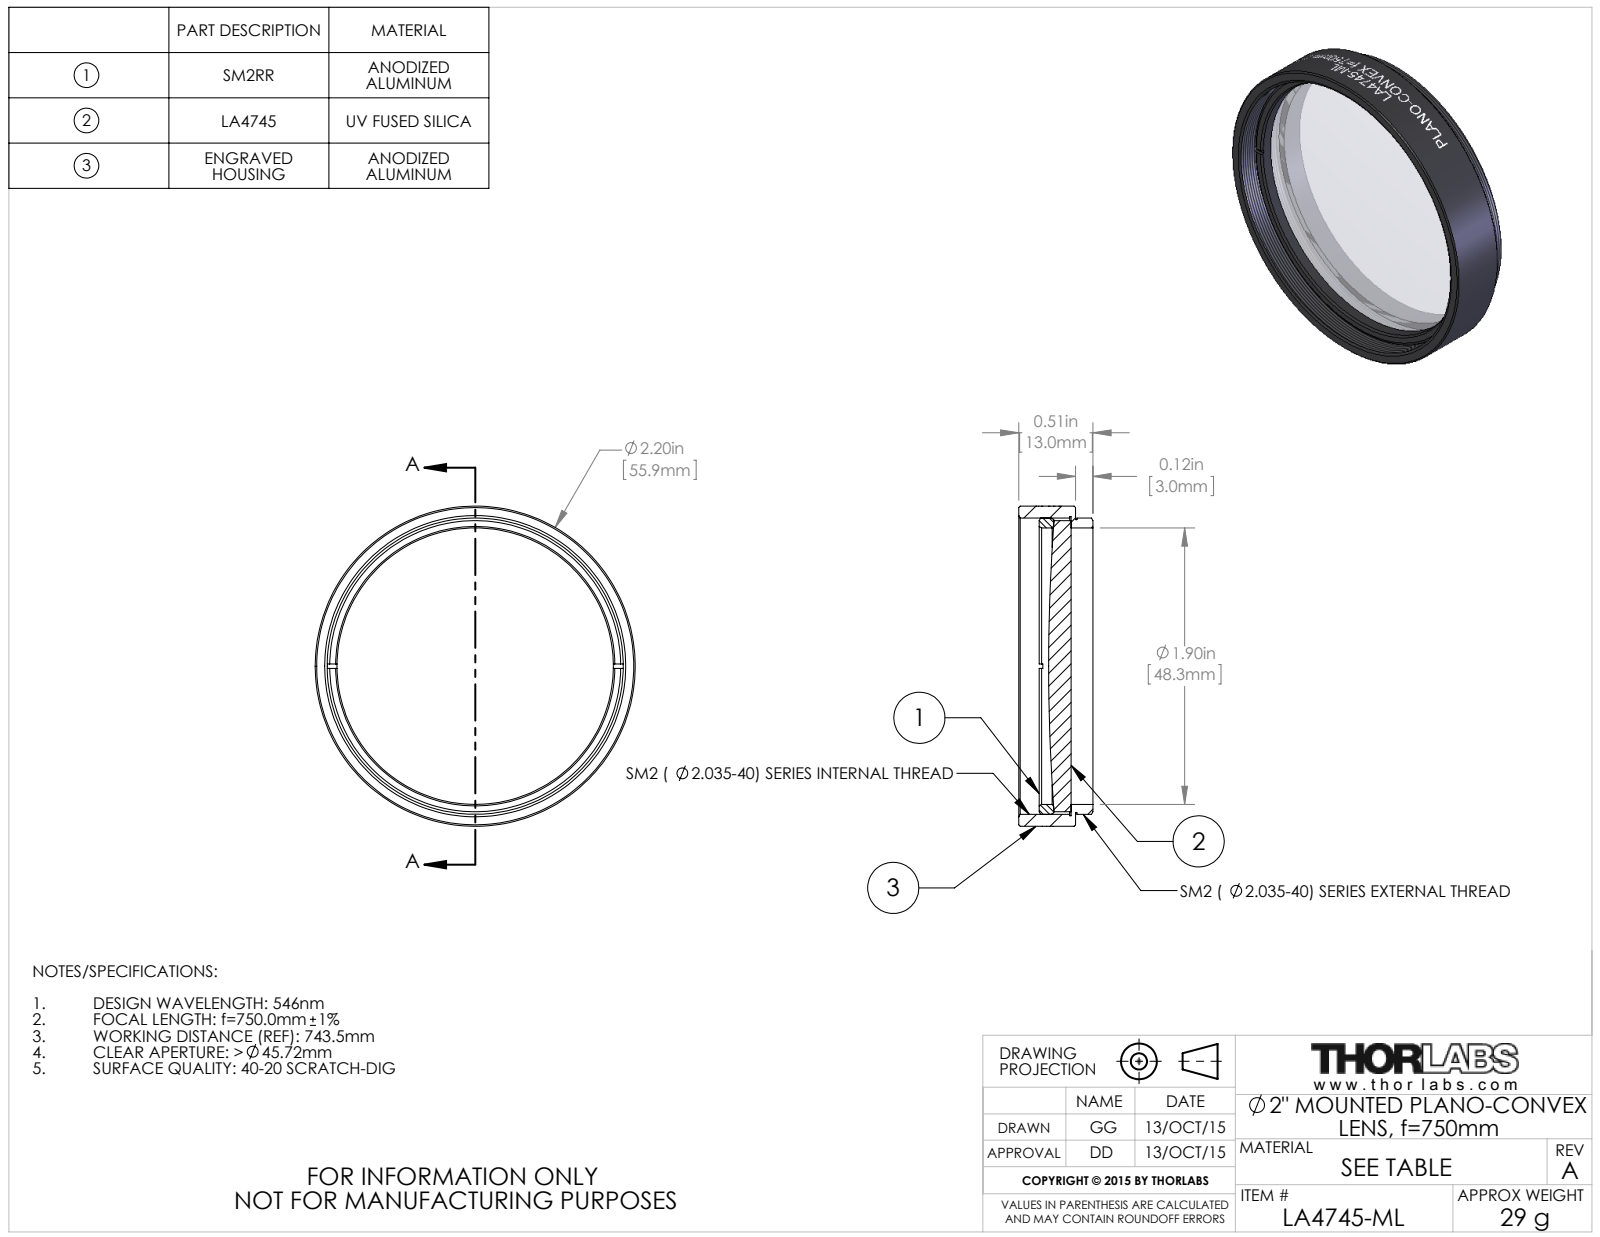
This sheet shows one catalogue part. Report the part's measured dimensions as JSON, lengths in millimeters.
{"part_name": "TTN039373-E0W", "step_written_by": "SolidWorks 2014 (CONFIG_CONTROL_DESIGN)", "units": "millimeters", "bodies": {"solids": 3, "faces": 108, "planar": 16, "cylindrical": 72, "other": 20}, "overall_size": [55.88, 55.88, 12.95], "volume_mm3": 12161, "surface_area_mm2": 11352, "round_holes": [[48.26, 1], [52.2, 1]], "round_bosses_or_shafts": [[55.88, 1], [51.69, 1], [51.18, 1], [50.8, 1]], "face_to_face_distances": [0.76, 9.91, 9.15, 3.05, 3.81, 12.96, 6.87, 3.82, 3.06, 6.09]}
